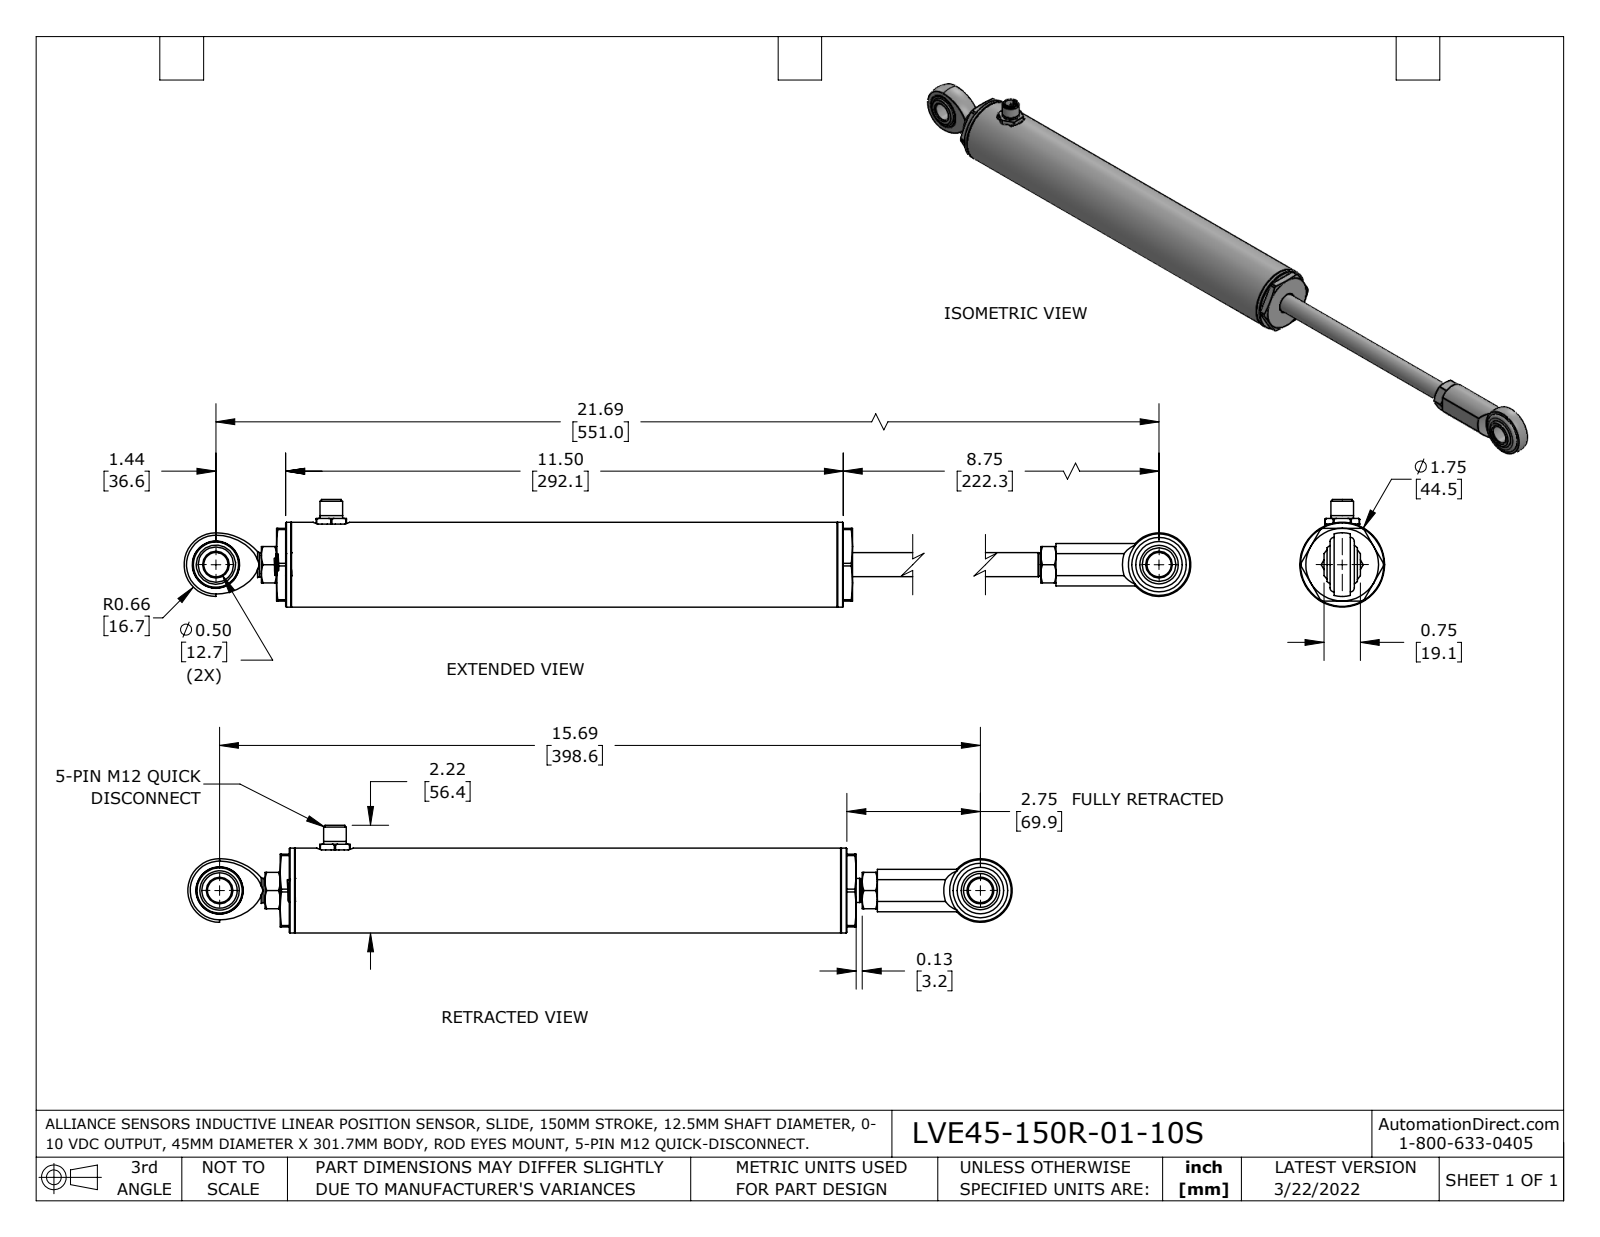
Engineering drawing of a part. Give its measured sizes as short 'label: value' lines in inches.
name: 3100-0025_9368T161; 3100-0012-YY; 3100-0174_9452K116; 3100-0023_9452K91 (+8 more)
written by: SolidWorks 2021 (AUTOMOTIVE_DESIGN)
unit: in
bodies: 23 solids, 873 faces (198 planar, 297 cylindrical, 378 other)
size: 23.004 × 2.219 × 1.75
volume: 15.76 in³; area: 229.1 in²
holes: 3× ⌀0.501, 1× ⌀0.197, 1× ⌀0.25, 1× ⌀0.264, 1× ⌀0.309, 1× ⌀0.329, 1× ⌀0.339, 1× ⌀0.413, 1× ⌀0.417, 1× ⌀0.453, 1× ⌀0.478, 1× ⌀0.5
bosses: 5× ⌀0.031, 1× ⌀1.75, 1× ⌀1.625, 1× ⌀1.562, 1× ⌀1.531, 1× ⌀1.5, 1× ⌀1.47, 1× ⌀1.384
rounds: 1× R0.325, 1× R0.354, 1× R0.378, 1× R0.38, 1× R0.438, 1× R0.85
face distances: 1.93, 0.5, 0.38, 0.69, 2.62, 9.573, 2.24, 1.55, 9.763, 9.073
hole spacings: 0.5, 21.693
